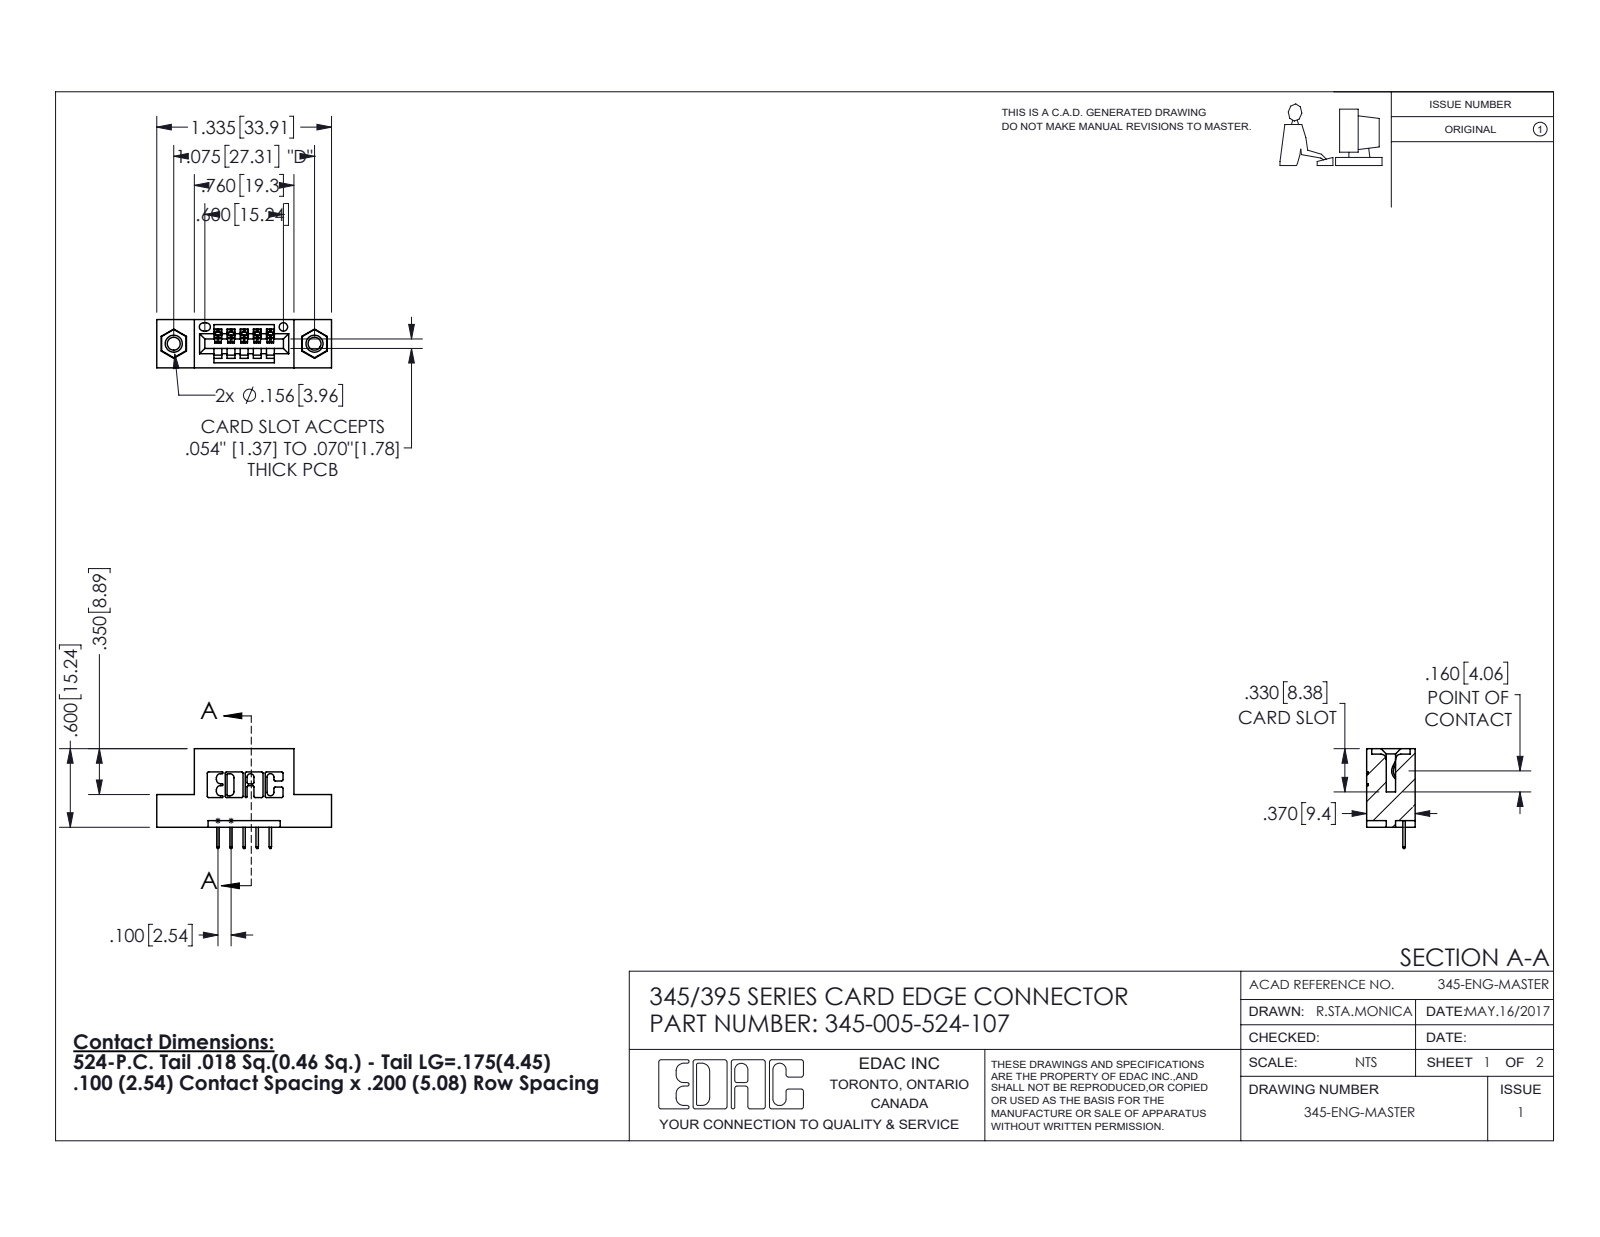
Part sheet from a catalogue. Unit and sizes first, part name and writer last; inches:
Units: inches
Overall size (bounding box): 1.335 × 0.762 × 0.37
Round holes (diameter × count): ⌀0.098 ×2, ⌀0.125 ×2, ⌀0.156 ×2, ⌀0.064 ×1
Round bosses / shafts (diameter × count): ⌀0.155 ×2
Partial cylindrical surfaces — rounded edges, fillets, slot ends (radius × count): R0.01 ×22, R0.006 ×10, R0.007 ×6, R0.031 ×6, R0.026 ×3, R0.031 ×2, R0.04 ×2, R0.014 ×1
Main face-to-face distances: 0.2, 0.37, 0.1, 0.072, 0.298, 0.35, 0.25, 0.06, 0.55, 0.025
Hole centre spacings: 0.27, 0.847, 1.075
Volume: 0.176 in³ · Surface area: 5.114 in²
Bodies: 8 solids, 496 faces (342 planar, 138 cylindrical, 16 other)
Part name (STEP PRODUCT): 345-005-524-107; 345 Part_Flush Mounting Lugs - 0.156 Dia-TI; 345-250-001_345-250-005-103; 345-292-001_345-293-124
STEP written by: SolidWorks 2016 (CONFIG_CONTROL_DESIGN)
